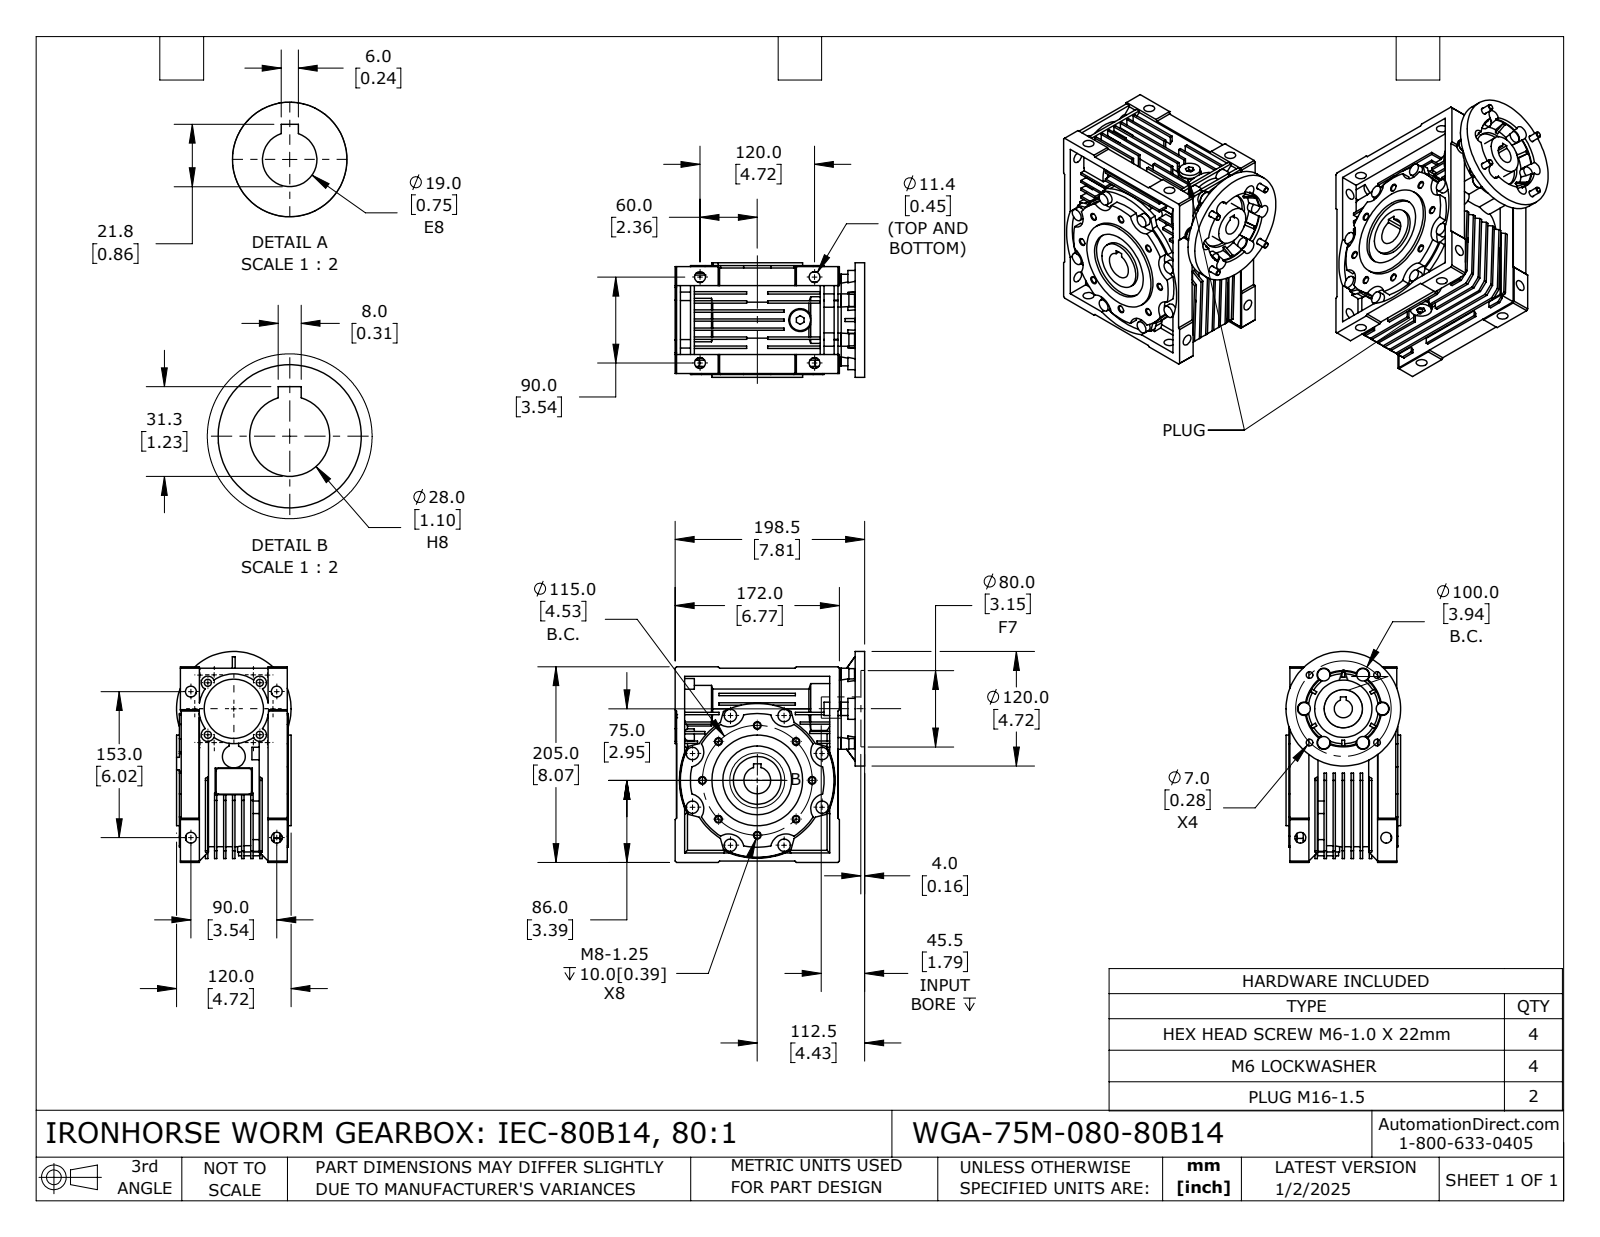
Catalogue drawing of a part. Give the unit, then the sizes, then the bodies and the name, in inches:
Units: inches
Overall size (bounding box): 8.701 × 8.228 × 4.724
Round holes (diameter × count): ⌀0.262 ×8, ⌀0.448 ×8, ⌀0.24 ×4, ⌀0.276 ×4, ⌀0.293 ×4, ⌀0.571 ×2, ⌀0.748 ×1, ⌀0.787 ×1, ⌀1.102 ×1, ⌀1.535 ×1, ⌀1.654 ×1, ⌀1.969 ×1
Round bosses / shafts (diameter × count): ⌀0.512 ×14, ⌀0.48 ×4, ⌀0.236 ×4, ⌀0.945 ×3, ⌀0.866 ×2, ⌀0.622 ×2, ⌀0.539 ×2, ⌀5.509 ×1
Partial cylindrical surfaces — rounded edges, fillets, slot ends (radius × count): R0.276 ×10, R0.63 ×8, R0.433 ×6, R0.098 ×4, R1.417 ×1, R1.437 ×1, R1.535 ×1, R1.575 ×1
Main face-to-face distances: 0.374, 0.098, 0.748, 0.472, 0.394, 0.276, 0.65, 1.122, 1.093, 0.846
Hole centre spacings: 1.733, 2.264, 2.485, 3.202, 4.183, 0.453, 1.515, 1.969
Volume: 174.1 in³ · Surface area: 745.4 in²
Bodies: 16 solids, 1304 faces (703 planar, 433 cylindrical, 168 other)
Part name (STEP PRODUCT): WGA-75M-080-80B14
STEP written by: SolidWorks 2024 (CONFIG_CONTROL_DESIGN)
